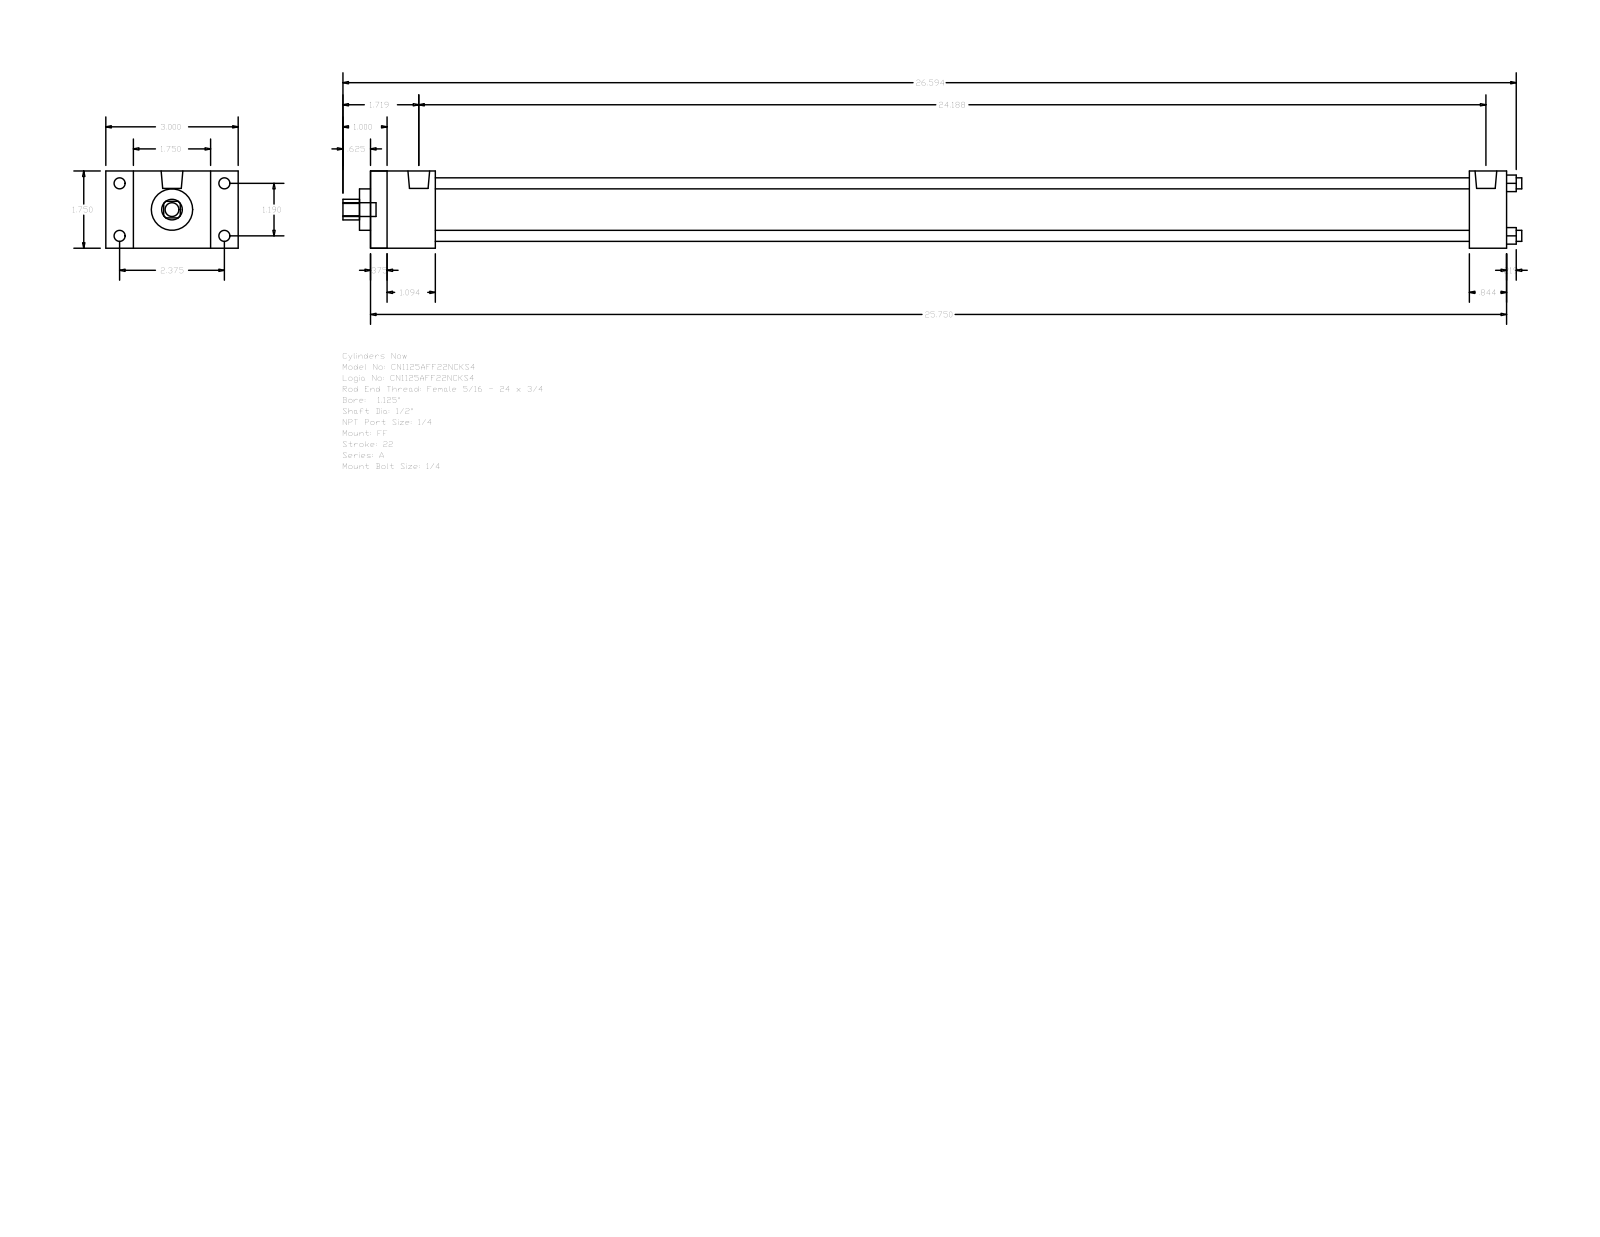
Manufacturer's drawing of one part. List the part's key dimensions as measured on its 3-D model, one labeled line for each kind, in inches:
Part name (STEP PRODUCT): A_FF__0112_0.5
STEP written by: GSSL Pune (CONFIG_CONTROL_DESIGN)
Units: inches
Bodies: 0 solids, 92 faces (64 planar, 28 cylindrical, 0 other)
Overall size (bounding box): 26.719 × 3 × 1.75
Round holes (diameter × count): ⌀0.25 ×4, ⌀0.5 ×1, ⌀0.937 ×1, ⌀1.255 ×1
Round bosses / shafts (diameter × count): ⌀0.25 ×4, ⌀0.219 ×4, ⌀0.492 ×2, ⌀0.313 ×1
Partial cylindrical surfaces — rounded edges, fillets, slot ends (radius × count): R0.234 ×1
Main face-to-face distances: 1.75, 25.75, 0.375, 25.375, 0.625, 24.906, 24.531, 0.844, 1.469, 1.094
Hole centre spacings: 0.841, 1.19, 1.683
